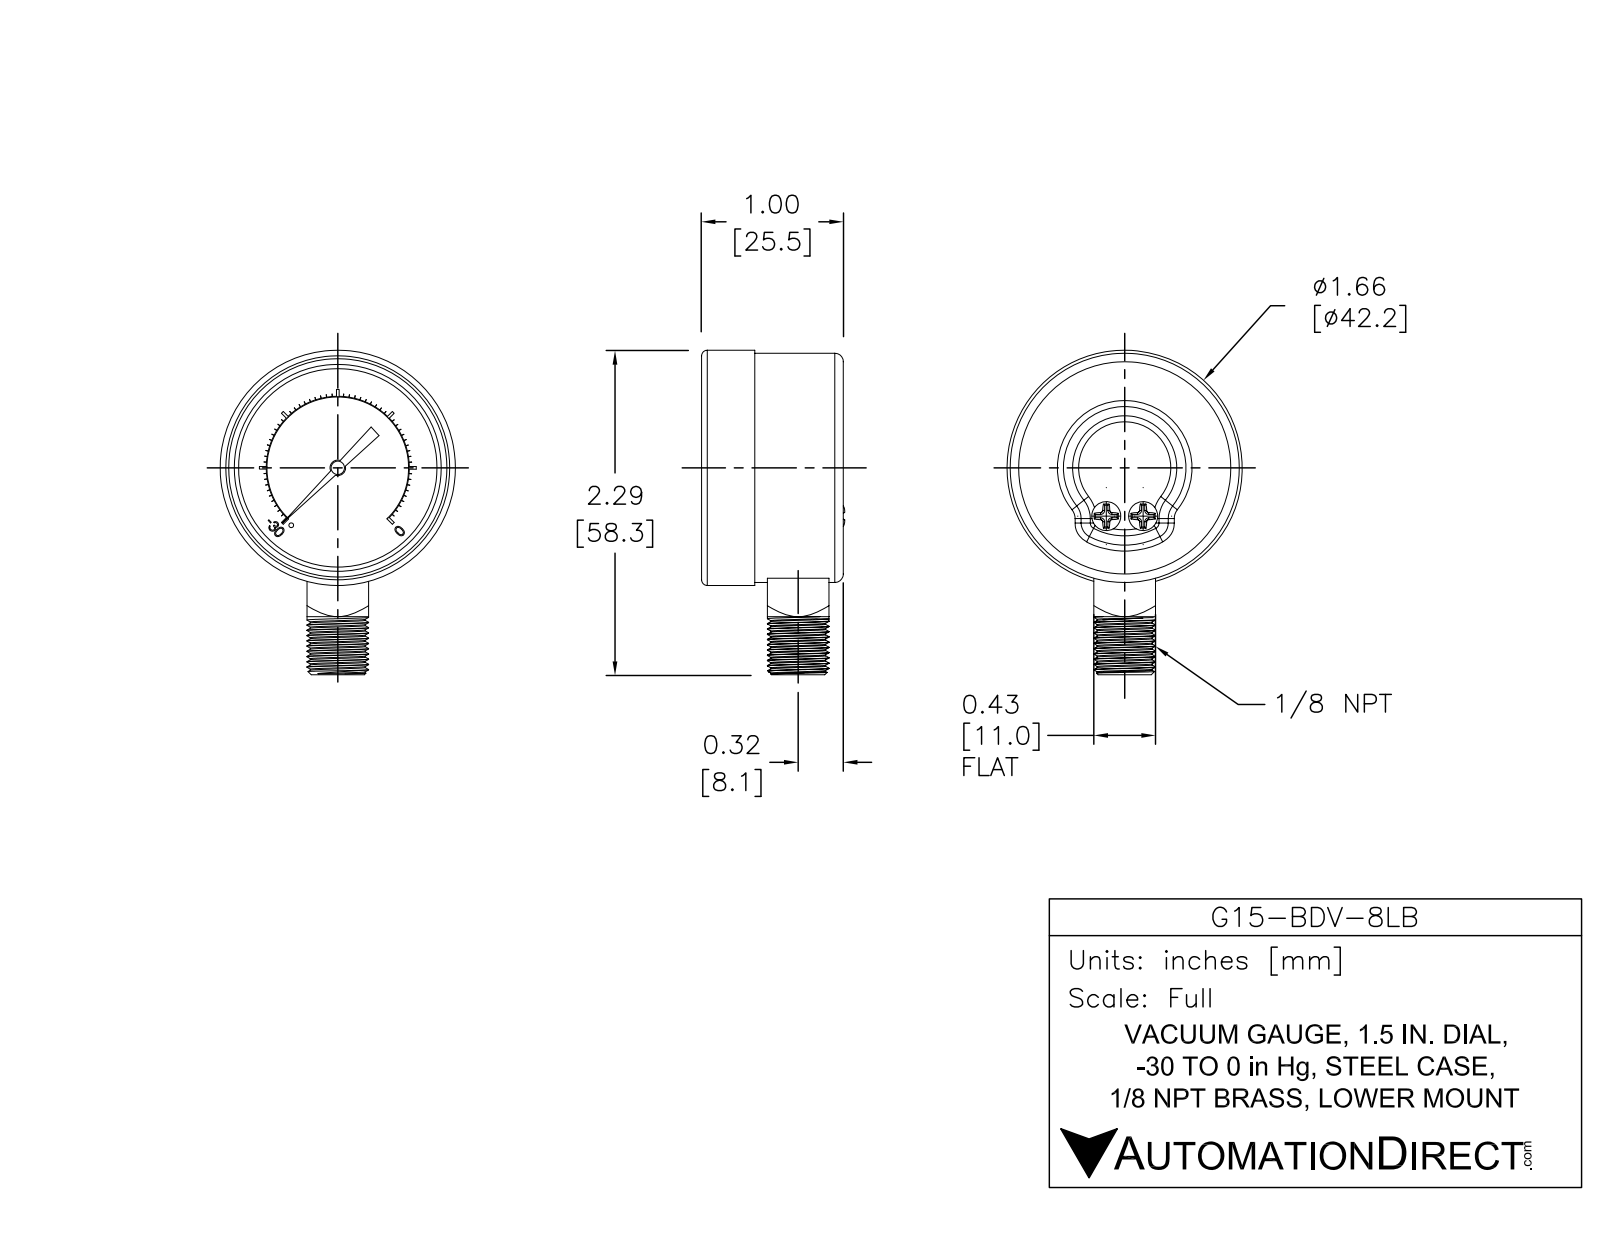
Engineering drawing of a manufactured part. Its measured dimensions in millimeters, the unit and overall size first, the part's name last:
Units: millimetres
Overall size (bounding box): 58.2 × 42.2 × 25.7
Round holes (diameter × count): ⌀3.6 ×1, ⌀35.6 ×1
Round bosses / shafts (diameter × count): ⌀5.2 ×2, ⌀42.2 ×1, ⌀41.1 ×1, ⌀11 ×1, ⌀2.8 ×1, ⌀2.4 ×1, ⌀0.8 ×1
Partial cylindrical surfaces — rounded edges, fillets, slot ends (radius × count): R1.5 ×4, R12.7 ×1, R12.8 ×1
Main face-to-face distances: 18, 2.5, 15.5, 11, 24.4, 21.8, 6.4, 1, 15.9, 13.3
Volume: 27 560 mm³ · Surface area: 7 774 mm²
Bodies: 1 solid, 422 faces (270 planar, 82 cylindrical, 70 other)
Part name (STEP PRODUCT): G15-BDV-8LB
STEP written by: SolidWorks 2021 (AUTOMOTIVE_DESIGN)
